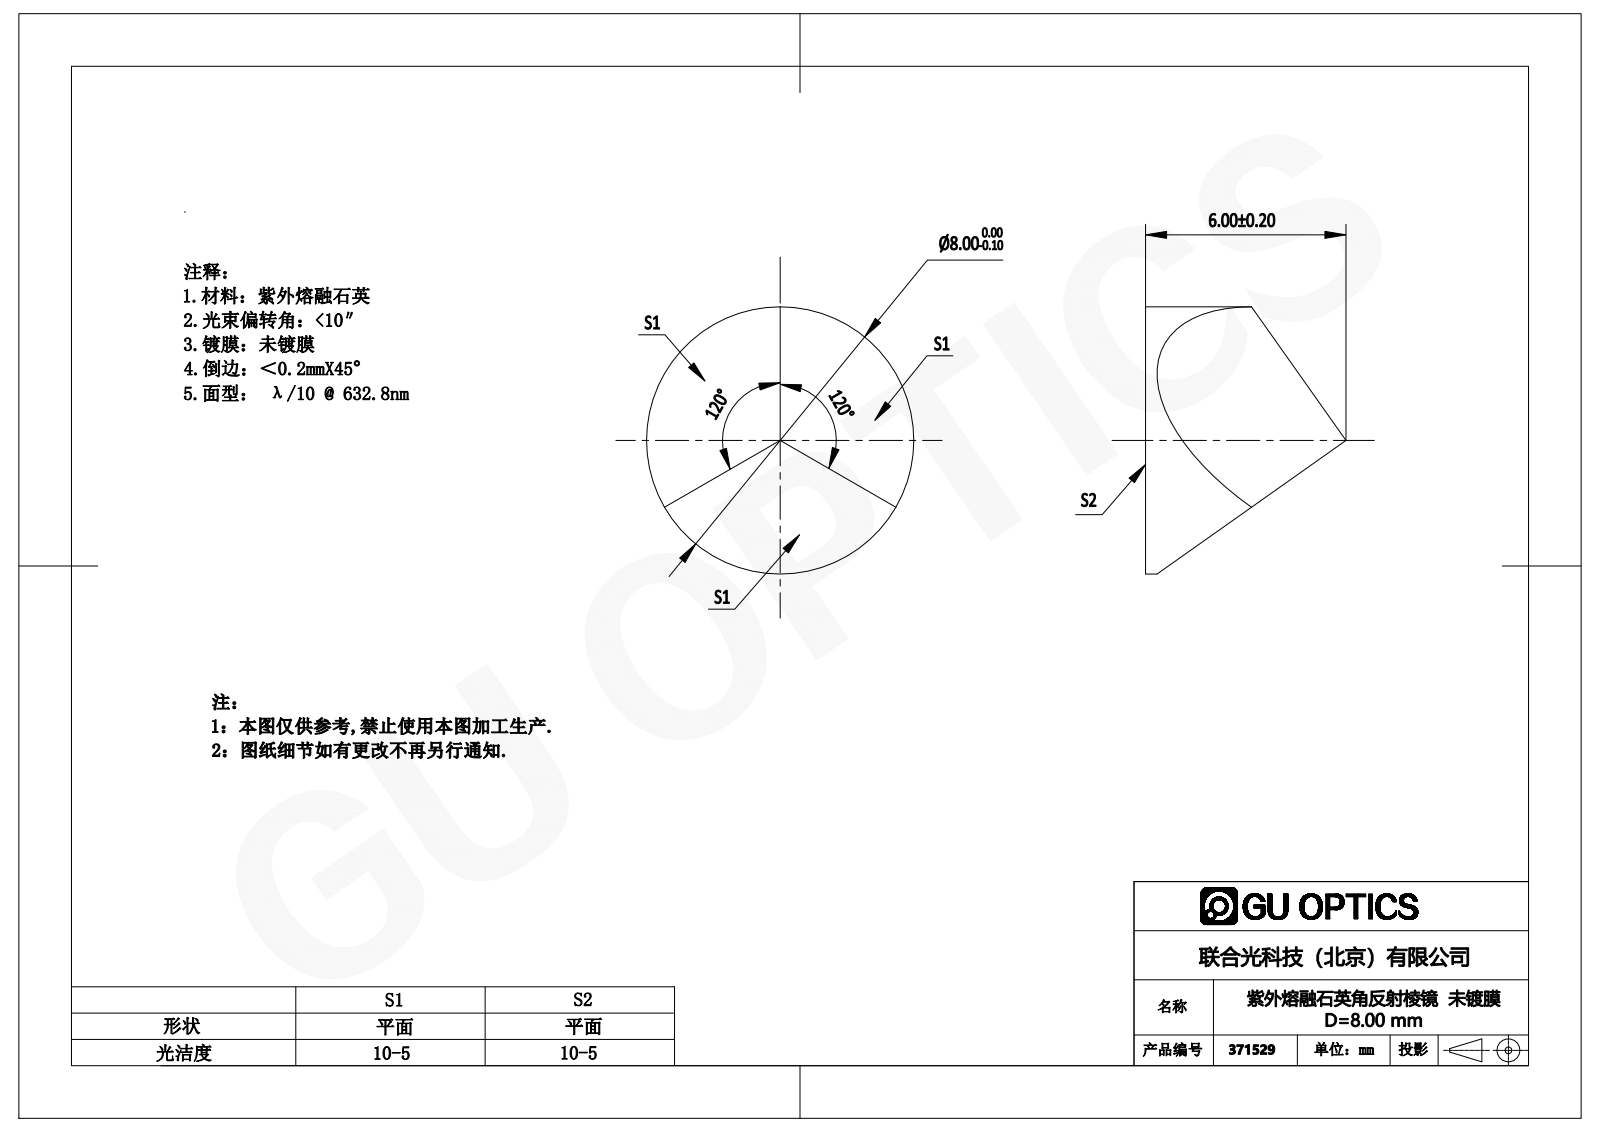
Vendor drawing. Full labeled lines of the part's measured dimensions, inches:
Part name (STEP PRODUCT): 371529
STEP written by: SolidWorks 2020 (CONFIG_CONTROL_DESIGN)
Units: inches
Bodies: 1 solid, 5 faces (4 planar, 1 cylindrical, 0 other)
Overall size (bounding box): 0.315 × 0.315 × 0.236
Volume: 0.009 in³ · Surface area: 0.265 in²
Round bosses / shafts (diameter × count): ⌀0.315 ×1
